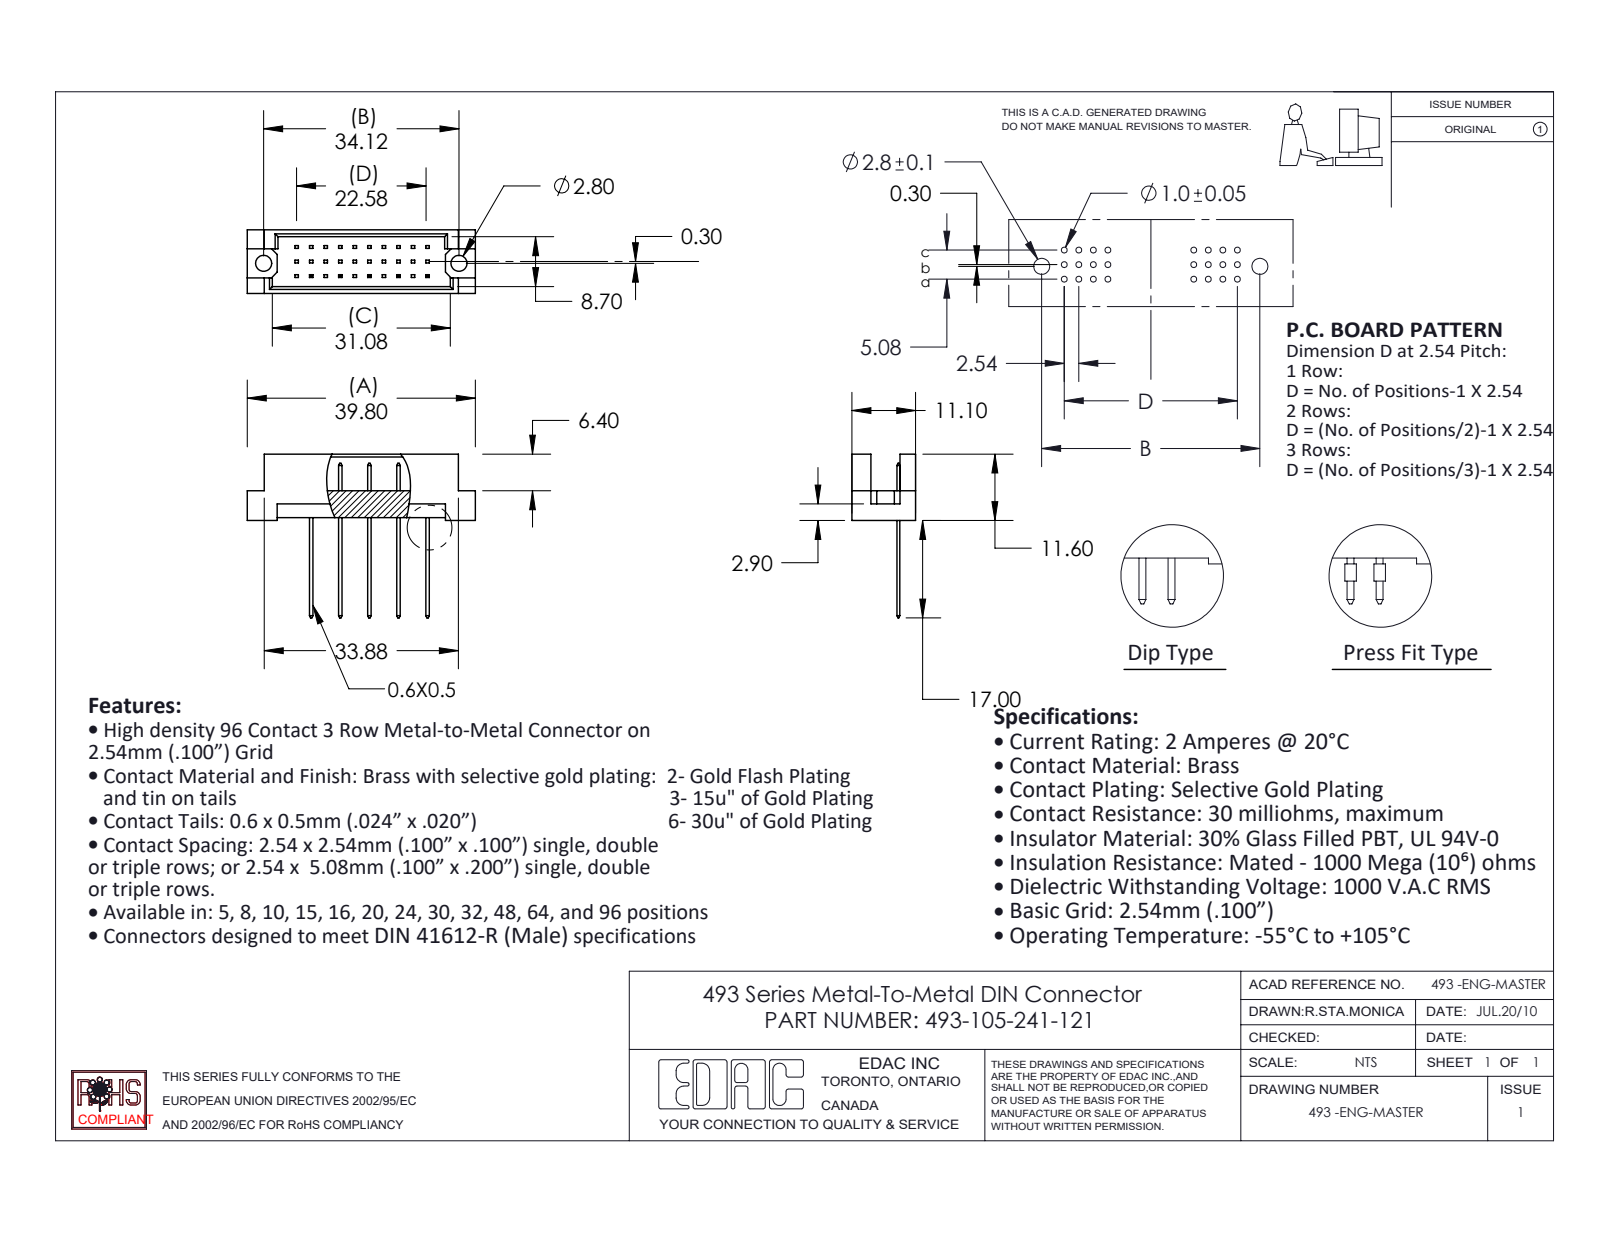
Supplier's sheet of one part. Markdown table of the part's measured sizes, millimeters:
| quantity | value |
| --- | --- |
| part name | 493-290_41; 493-105-241-121; 493 Part_30 |
| STEP written by | SolidWorks 2020 (CONFIG_CONTROL_DESIGN) |
| units | millimeters |
| bodies | 6 solids, 242 faces (238 planar, 4 cylindrical, 0 other) |
| overall size | 39.8 × 28.6 × 11.1 |
| volume | 2 413 mm³ |
| surface area | 3 033 mm² |
| round holes (diameter × count) | 2.8 × 2 |
| main face-to-face distances | 1.2, 9.9, 11.1, 8.7, 0.5, 5.08, 4.7, 2.76, 3.26, 7.84 |
| hole center spacings | 34.12 |
